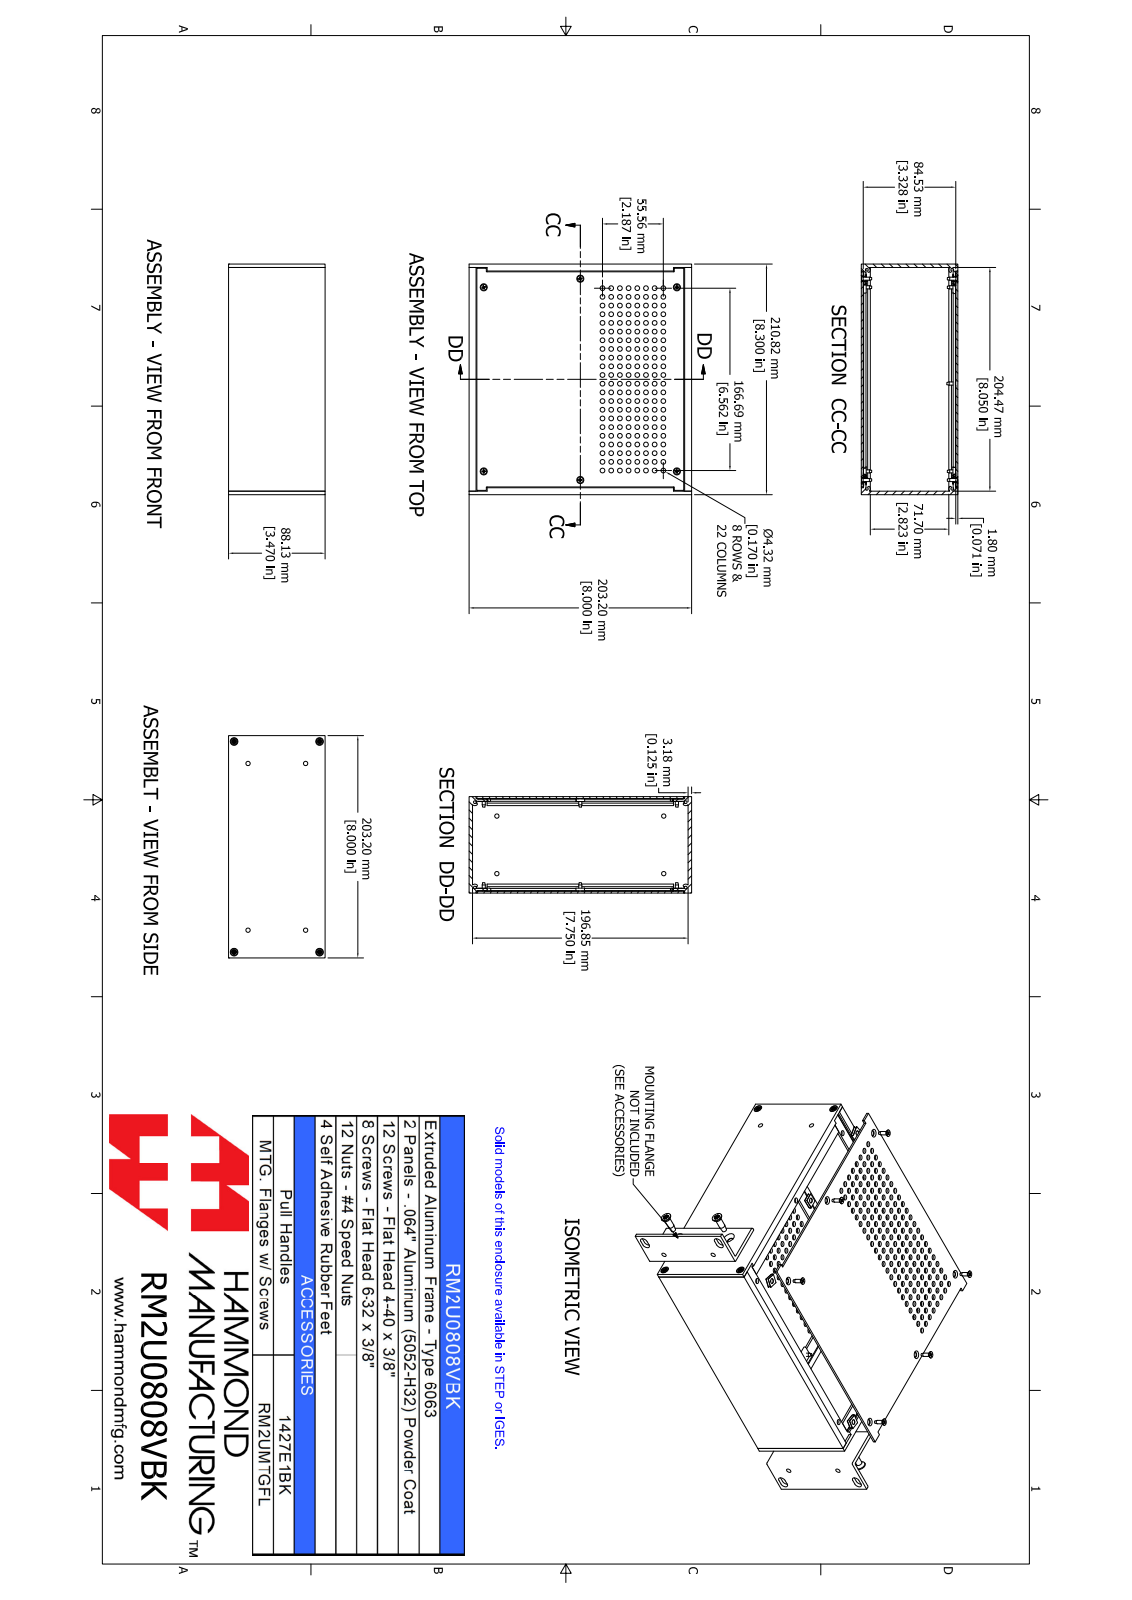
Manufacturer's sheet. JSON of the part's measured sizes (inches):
{"part_name": "RM2U0808VBK", "step_written_by": "SolidWorks 2021 (AUTOMOTIVE_DESIGN)", "units": "inches", "bodies": {"solids": 39, "faces": 1355, "planar": 478, "cylindrical": 510, "other": 367}, "overall_size": [8.3, 8, 3.47], "volume_in3": 25.63, "surface_area_in2": 558, "round_holes": [[0.17, 176], [0.098, 6], [0.157, 6], [0.169, 6], [0.138, 4], [0.156, 4]], "round_bosses_or_shafts": [[0.214, 7], [0.112, 7], [0.238, 4], [0.138, 4]], "partial_cylinders_radius": [[0.039, 12], [0.049, 12], [0.05, 8], [0.125, 8], [0.037, 6], [0.038, 4]], "face_to_face_distances": [0.071, 3.399, 0.125, 3.47, 3.328, 7.875, 8, 0.125, 8.3, 8.05], "hole_center_spacings": [0.313, 0.699, 0.442, 1.289, 0.988, 1.25, 0.937, 0.625]}
